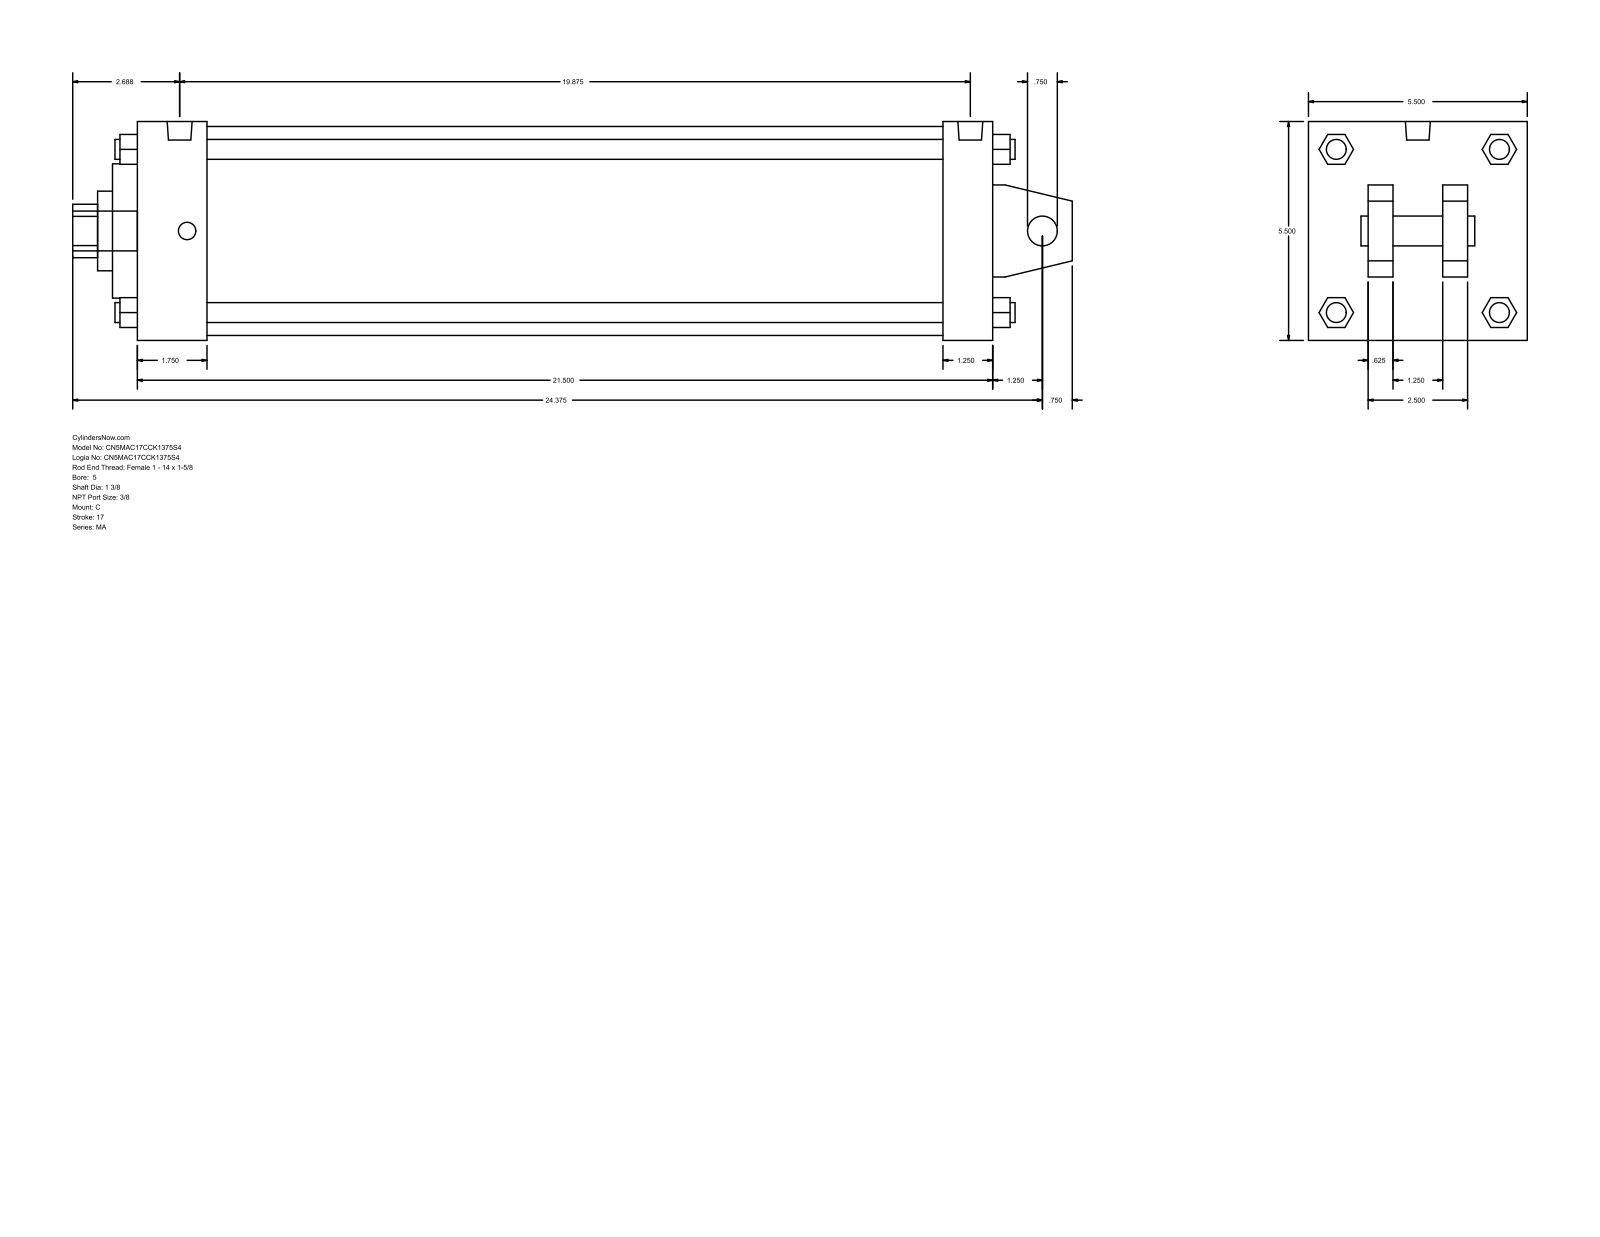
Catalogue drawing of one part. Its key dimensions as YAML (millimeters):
part_name: "MA_C__0500_1.375"
step_written_by: "GSSL Pune (CONFIG_CONTROL_DESIGN)"
units: millimeters
bodies: {solids: 0, faces: 141, planar: 109, cylindrical: 32, other: 0}
overall_size: [638.17, 139.7, 139.7]
round_holes:
  - {diameter: 19.05, count: 1}
  - {diameter: 34.92, count: 1}
  - {diameter: 50.8, count: 1}
  - {diameter: 85.72, count: 1}
  - {diameter: 133.35, count: 1}
round_bosses_or_shafts:
  - {diameter: 12.7, count: 4}
  - {diameter: 11.11, count: 4}
  - {diameter: 15.93, count: 2}
  - {diameter: 25.4, count: 1}
partial_cylinders:
  - {radius: 17.06, count: 1}
face_to_face_distances: [139.7, 546.11, 15.87, 31.76, 514.35, 44.45, 469.9, 501.66, 38.1, 101.6]
